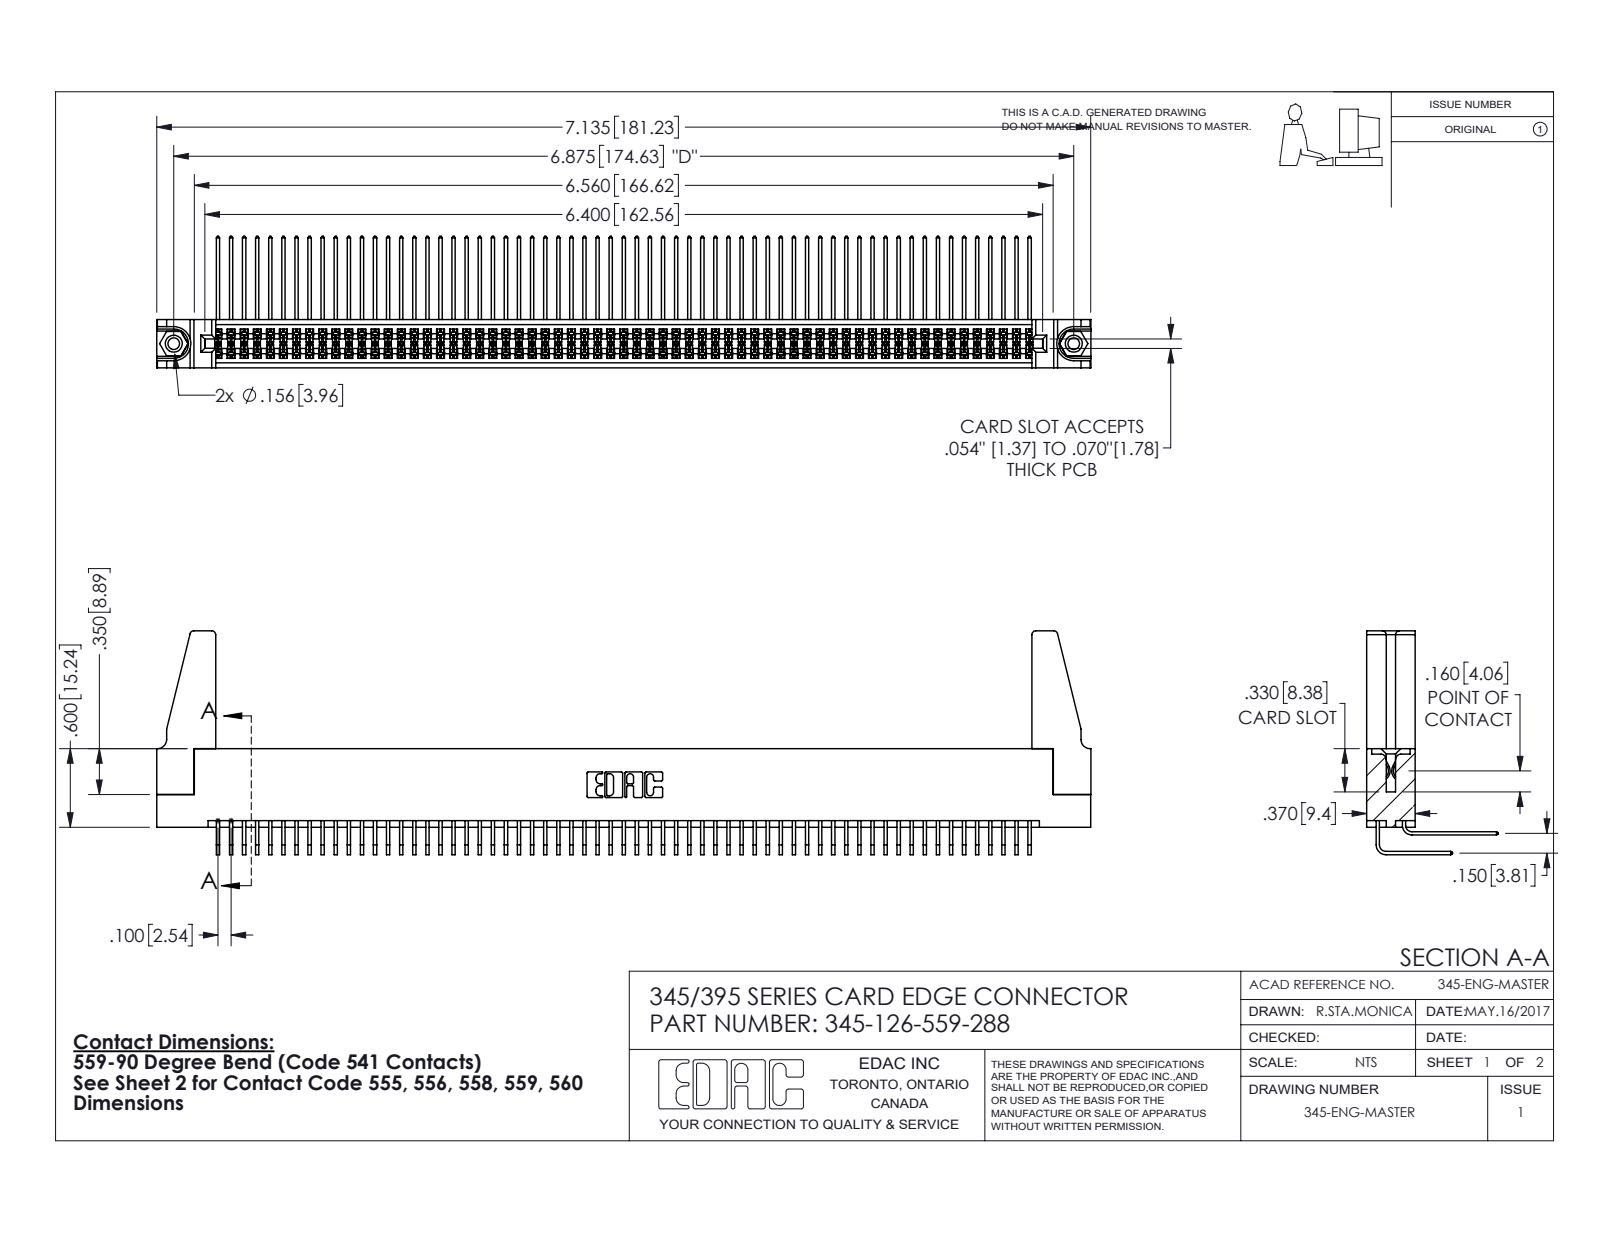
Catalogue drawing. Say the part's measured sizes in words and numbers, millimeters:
The part is named "345-292-001_558 559 Tail - 1; 345-292-001_559 Tail - 2; 345-250-001_345-250-001-102; 345 Part_Flush Mounting Lugs - 0.156 Dia-TH (+2 more)". Its 3-D file was written by "SolidWorks 2016 (CONFIG_CONTROL_DESIGN)". It is 131 solids with 6802 faces: 4562 planar, 2224 cylindrical and 16 other. Overall it measures 181.3 by 43.4 by 25.5 millimeters. Its volume is 21 780 cubic millimeters and its surface area 34 340 square millimeters. Round holes: 2 of diameter 2.3, 2 of diameter 3.2, 2 of diameter 4, 1 of diameter 1.6. Round bosses or shafts: 2 of diameter 3.9. Partial cylindrical surfaces (rounded edges, fillets, slot ends): 251 of radius 0.2, 22 of radius 0.3, 8 of radius 0.8, 6 of radius 0.2, 6 of radius 0.8, 3 of radius 0.7, 2 of radius 0.4, 2 of radius 0.5. The main face-to-face distances are 1.8, 7.6, 9.4, 5.1, 2.5, 6.9, 0.6, 5.7, 4.4, 3.8. The hole center spacings are 6.9, 168.6, 174.6.
